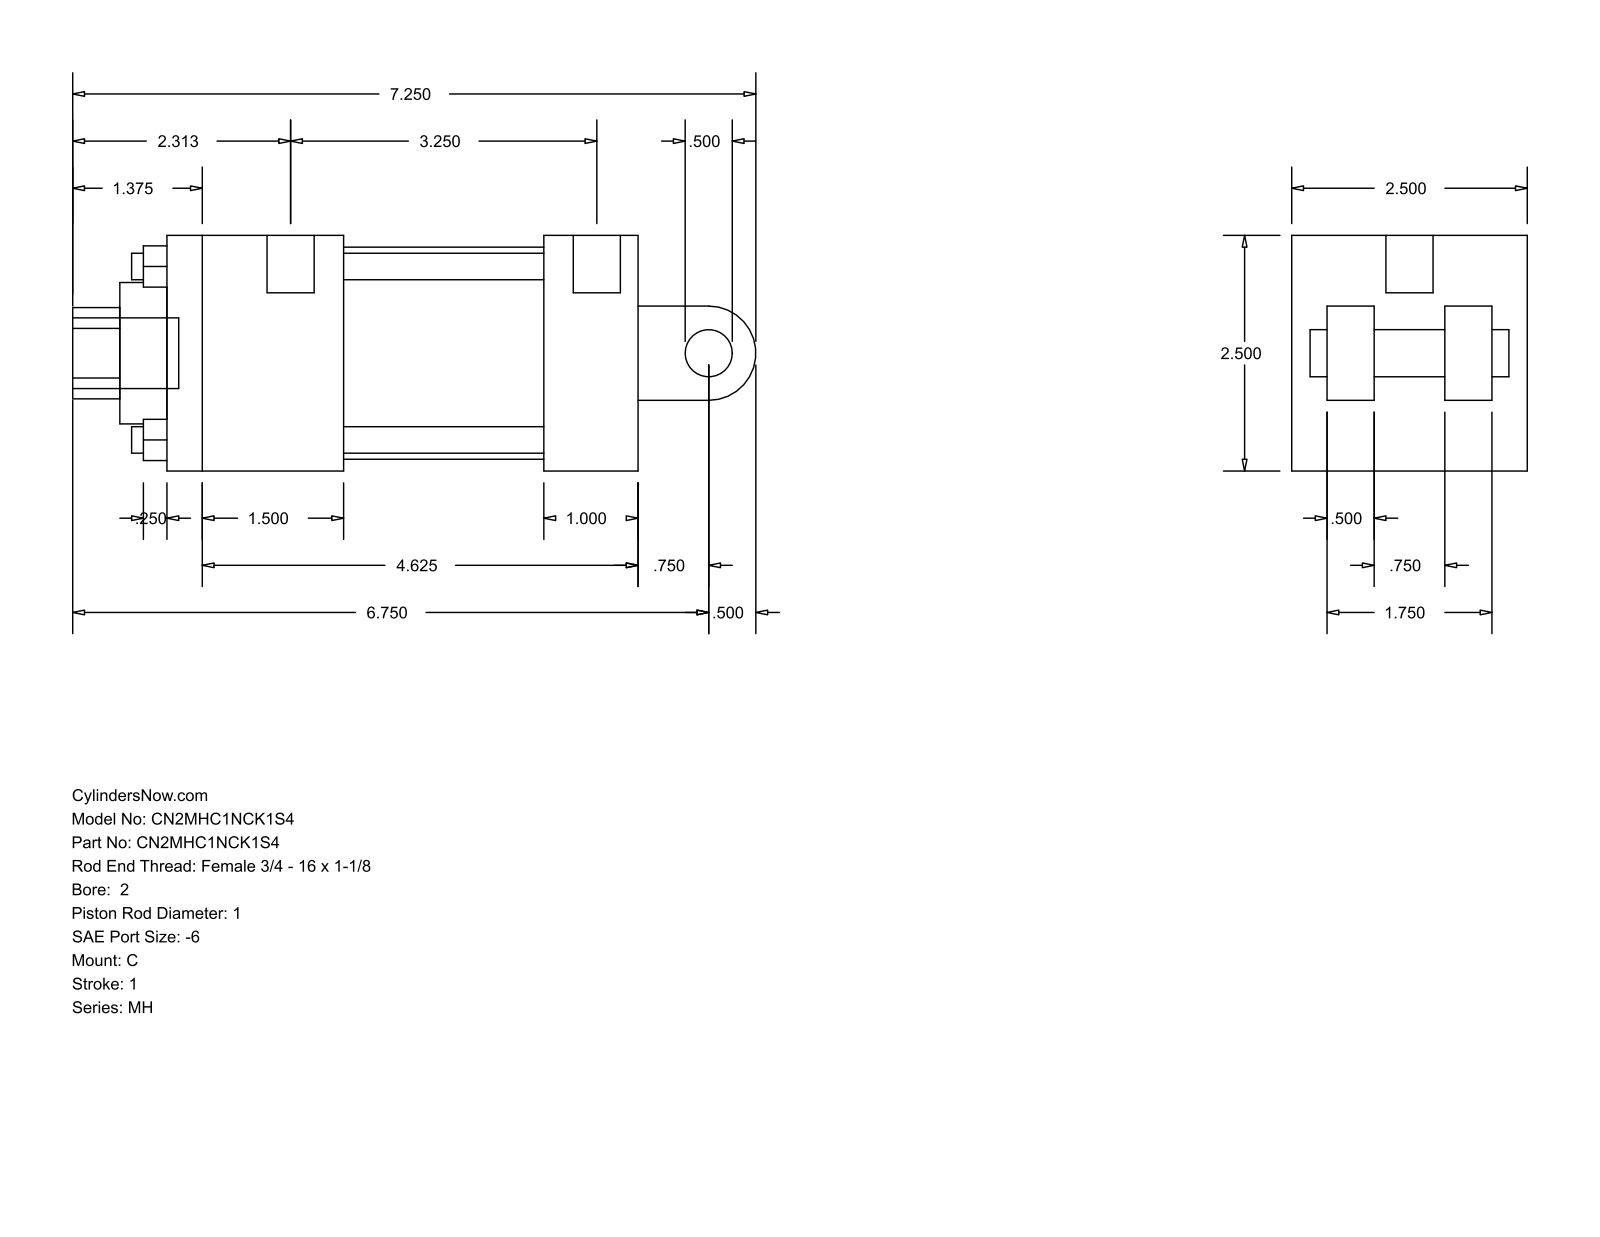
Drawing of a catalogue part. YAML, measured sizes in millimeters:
part_name: "MH_C__0200_1"
step_written_by: "GSSL Pune (CONFIG_CONTROL_DESIGN)"
units: millimeters
bodies: {solids: 0, faces: 99, planar: 70, cylindrical: 29, other: 0}
overall_size: [184.15, 63.5, 63.5]
round_holes:
  - {diameter: 7.14, count: 4}
  - {diameter: 5.56, count: 2}
  - {diameter: 12.7, count: 1}
  - {diameter: 25.4, count: 1}
  - {diameter: 38.1, count: 1}
  - {diameter: 57.15, count: 1}
round_bosses_or_shafts:
  - {diameter: 12.7, count: 2}
  - {diameter: 5.56, count: 2}
  - {diameter: 19.05, count: 1}
partial_cylinders:
  - {radius: 12.29, count: 1}
  - {radius: 12.7, count: 1}
face_to_face_distances: [63.5, 127, 12.7, 25.4, 9.52, 47.63, 53.98, 101.6, 53.97, 79.37]
hole_center_spacings: [33.05, 46.74, 66.1, 3.17]
